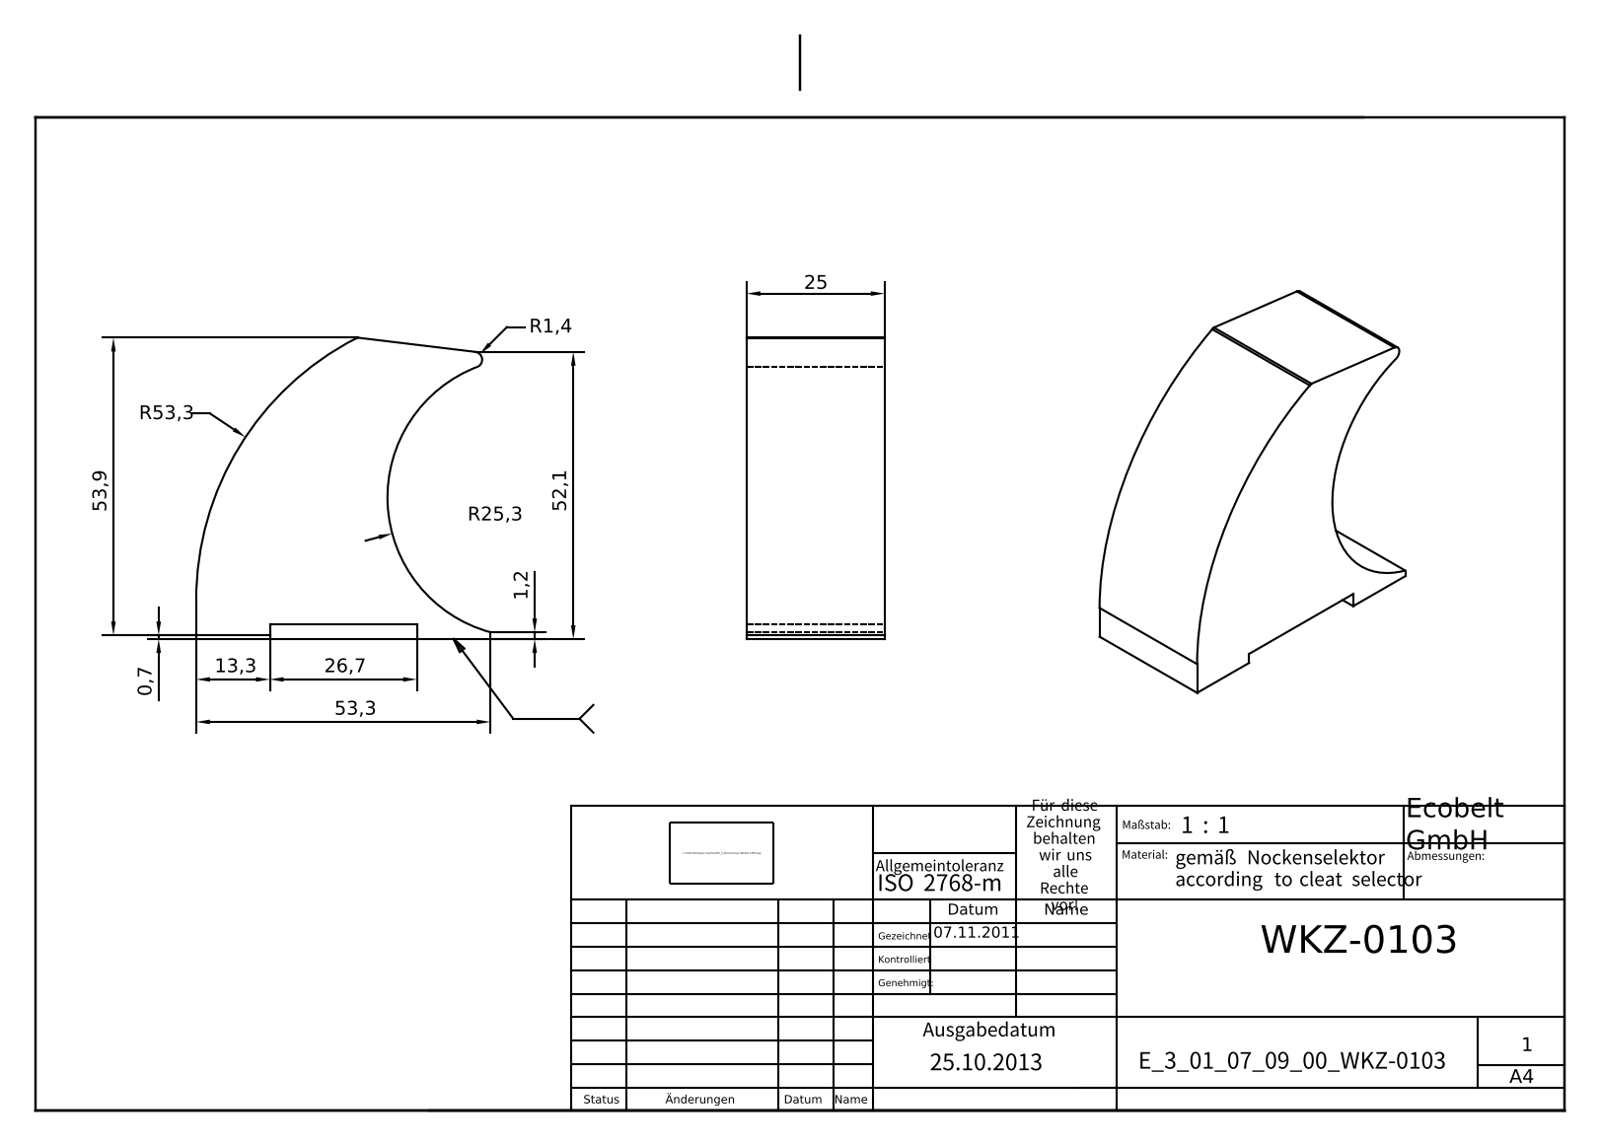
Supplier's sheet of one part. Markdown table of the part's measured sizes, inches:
| quantity | value |
| --- | --- |
| part name | E_3_01_07_09_00_WKZ-0103 |
| STEP written by | Autodesk Inventor 2025 (AUTOMOTIVE_DESIGN) |
| units | inches |
| bodies | 1 solid, 14 faces (11 planar, 3 cylindrical, 0 other) |
| overall size | 2.151 × 2.1 × 0.984 |
| volume | 2.629 in³ |
| surface area | 13.6 in² |
| partial cylindrical surfaces (radius × count) | 0.056 × 1, 0.997 × 1, 2.1 × 1 |
| main face-to-face distances | 0.984, 0.106, 0.028, 0.079, 1.575, 0.525, 1.05, 2.1 |
